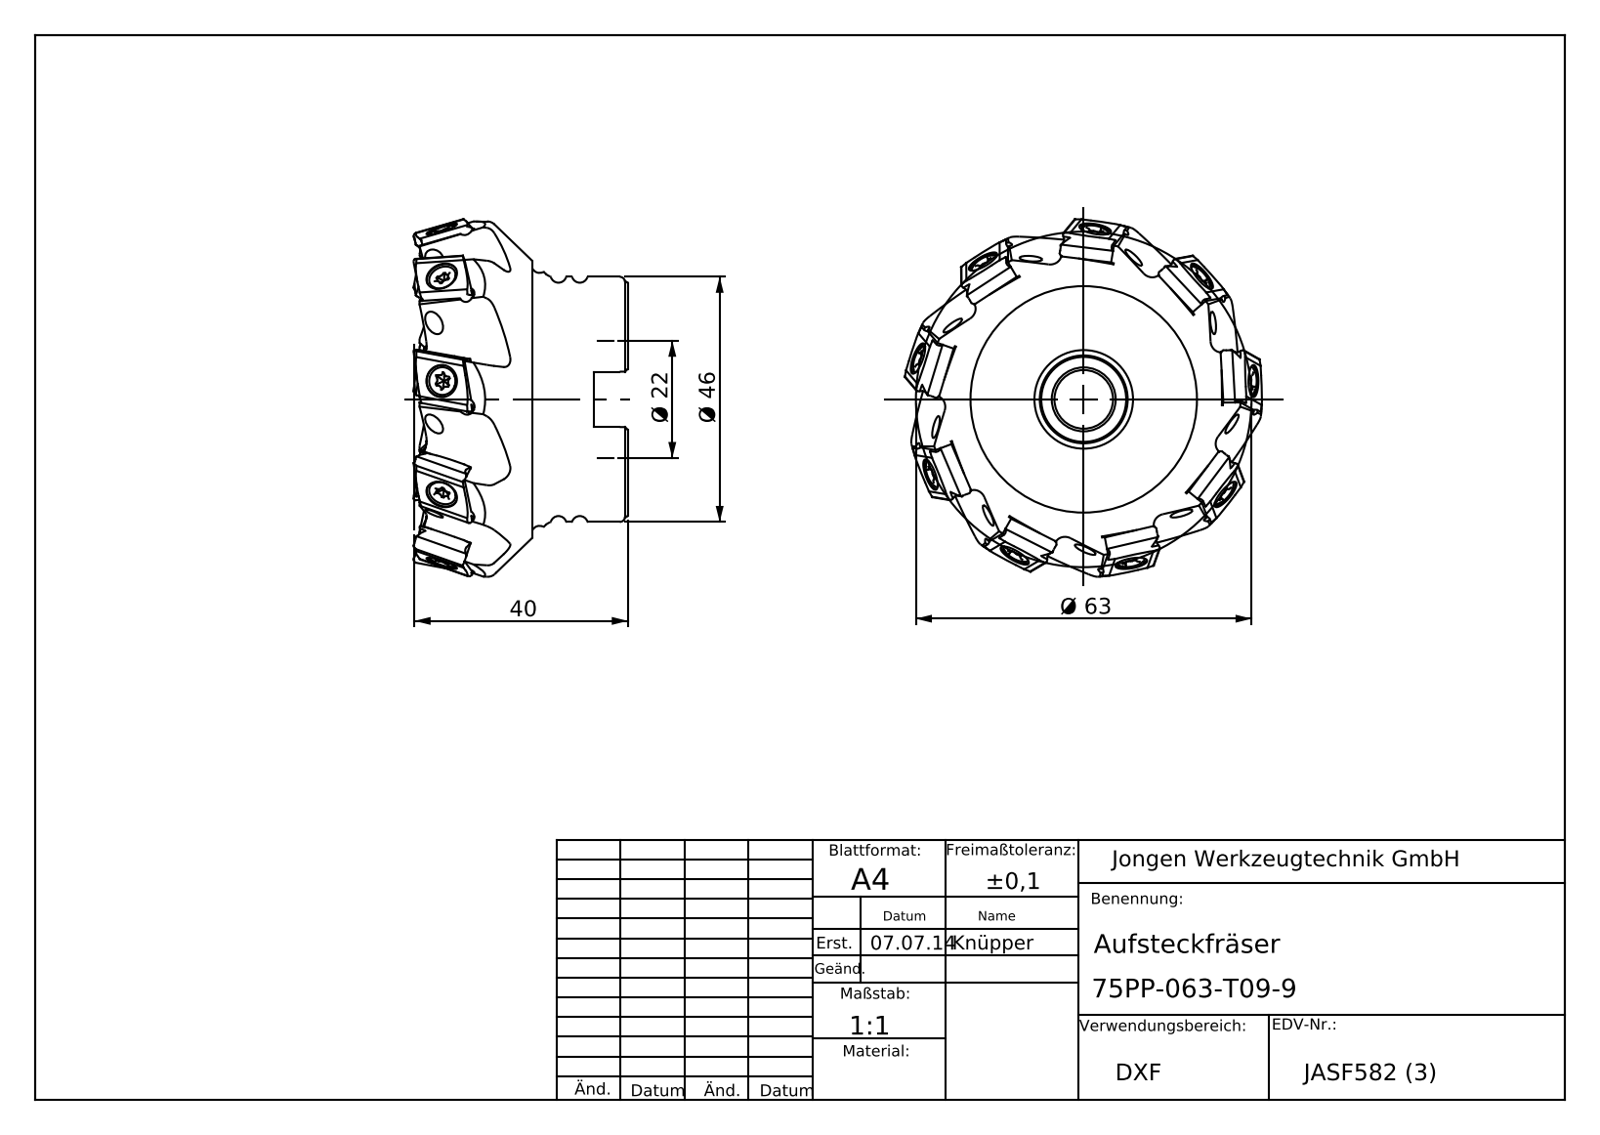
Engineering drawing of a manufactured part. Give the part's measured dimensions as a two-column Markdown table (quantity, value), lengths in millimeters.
| quantity | value |
| --- | --- |
| part name | 75PP_063_T09_9 |
| STEP written by | SolidWorks 2015 (AUTOMOTIVE_DESIGN) |
| units | millimeters |
| bodies | 1 solid, 187 faces (69 planar, 52 cylindrical, 66 other) |
| overall size | 68.29 × 68.29 × 40.03 |
| volume | 75 362 mm³ |
| surface area | 18 269 mm² |
| round holes (diameter × count) | 3 × 9, 3.3 × 9, 11 × 1, 16.5 × 1, 22 × 1, 22.15 × 1, 22.3 × 1 |
| round bosses / shafts (diameter × count) | 46 × 1 |
| partial cylindrical surfaces (radius × count) | 1.5 × 9, 2 × 9, 33.4 × 1 |
| main face-to-face distances | 35.9, 6.3, 29.6, 20, 13.7, 15.9, 5.7, 10.4, 25.4, 19.1 |
